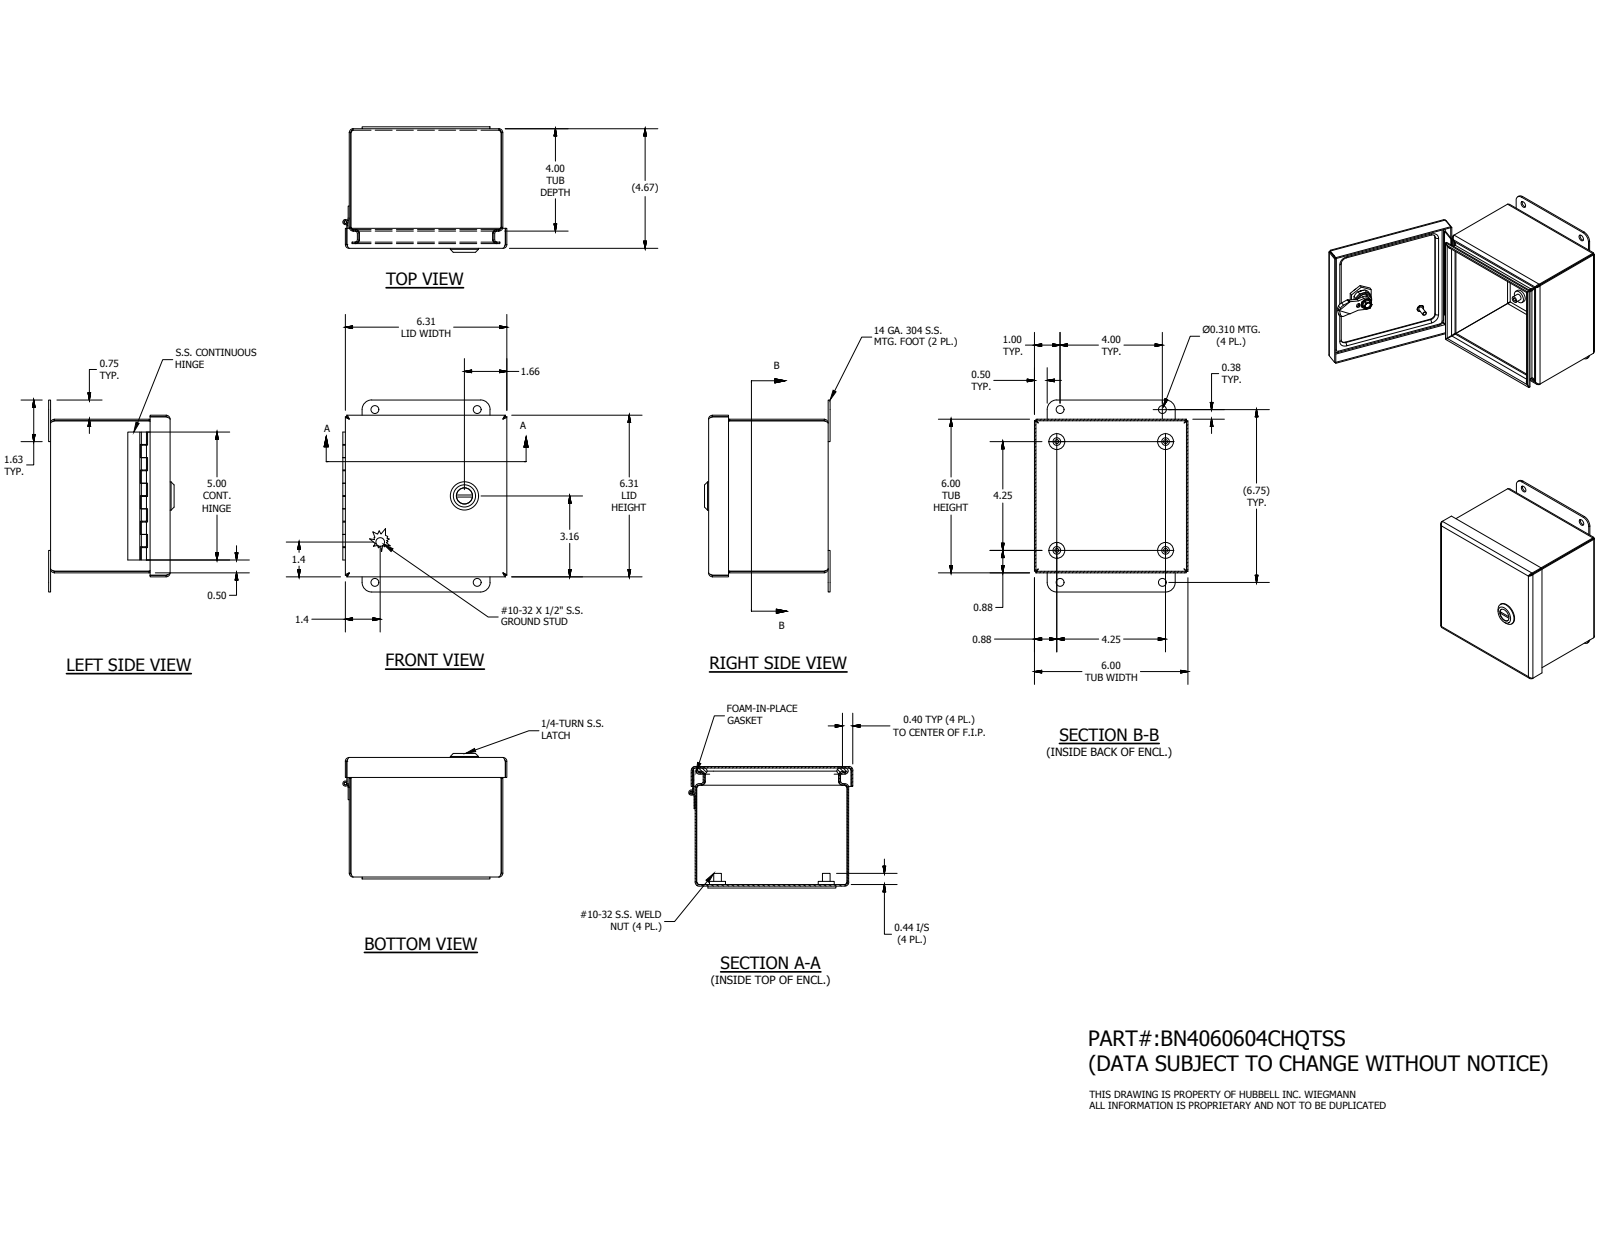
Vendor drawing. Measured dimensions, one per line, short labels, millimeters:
name: BN40606CHQTSSLID; 6x6; 34853; H4050545LH (+8 more)
written by: Autodesk Inventor 2016 (AUTOMOTIVE_DESIGN)
unit: mm
bodies: 19 solids, 568 faces (299 planar, 175 cylindrical, 94 other)
size: 190.5 × 162.86 × 124.59
volume: 268 930 mm³; area: 326 940 mm²
holes: 4× ⌀3.96, 4× ⌀7.87, 1× ⌀2.96, 1× ⌀5, 1× ⌀8, 1× ⌀10, 1× ⌀10.2, 1× ⌀16.1
bosses: 4× ⌀15.88, 4× ⌀7.62, 1× ⌀28, 1× ⌀19.8, 1× ⌀16, 1× ⌀15.2, 1× ⌀13.5, 1× ⌀12.8
rounds: 20× R2.38, 20× R3.88, 16× R3.17, 8× R0.5, 4× R4, 4× R9.53, 2× R2.31, 1× R6.45
face distances: 1.5, 150.9, 1.49, 152.4, 117.19, 118.68, 115.69, 117.18, 149.41, 150.91
hole spacings: 31.91, 107.95, 109.48, 139.74, 101.6, 152.66, 171.45, 174.62
